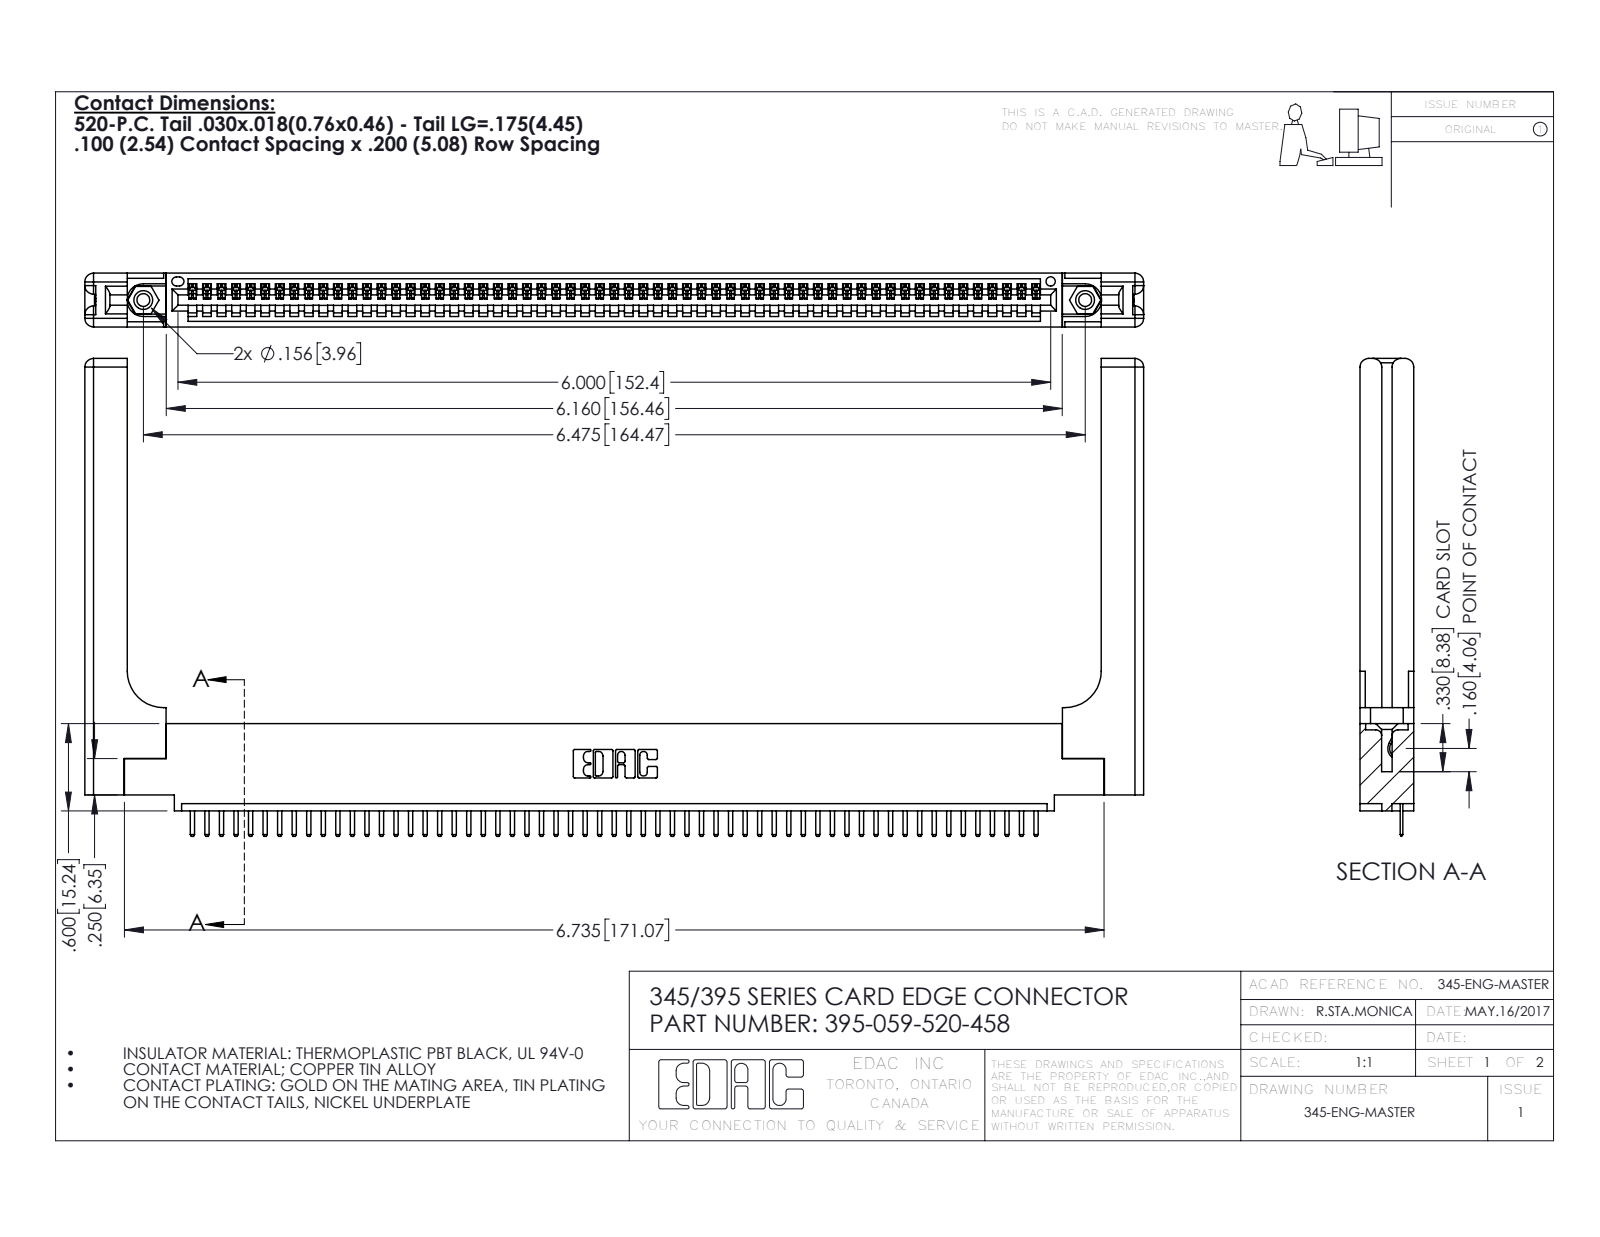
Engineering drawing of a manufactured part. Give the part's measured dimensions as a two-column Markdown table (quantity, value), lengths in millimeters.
| quantity | value |
| --- | --- |
| part name | 345-250-001_345-250-001-102; 345-292-001_345-293-120; 395-059-520-458; 345-220-058_345-220-058 (+1 more) |
| STEP written by | SolidWorks 2016 (CONFIG_CONTROL_DESIGN) |
| units | millimeters |
| bodies | 64 solids, 4044 faces (2710 planar, 1274 cylindrical, 60 other) |
| overall size | 184.9 × 83.4 × 9.4 |
| volume | 25 960 mm³ |
| surface area | 28 260 mm² |
| round holes (diameter × count) | 2.3 × 2, 3.2 × 2, 4 × 2, 1.6 × 1 |
| round bosses / shafts (diameter × count) | 3.9 × 2 |
| partial cylindrical surfaces (radius × count) | 0.3 × 120, 0.2 × 118, 0.3 × 22, 1.5 × 16, 0.2 × 6, 0.8 × 6, 0.7 × 3, 0.8 × 2 |
| main face-to-face distances | 1.8, 9.4, 7.6, 2.5, 6.9, 0.6, 5.1, 5.7, 3.8, 3.8 |
| hole center spacings | 6.9, 158.5, 164.5 |
